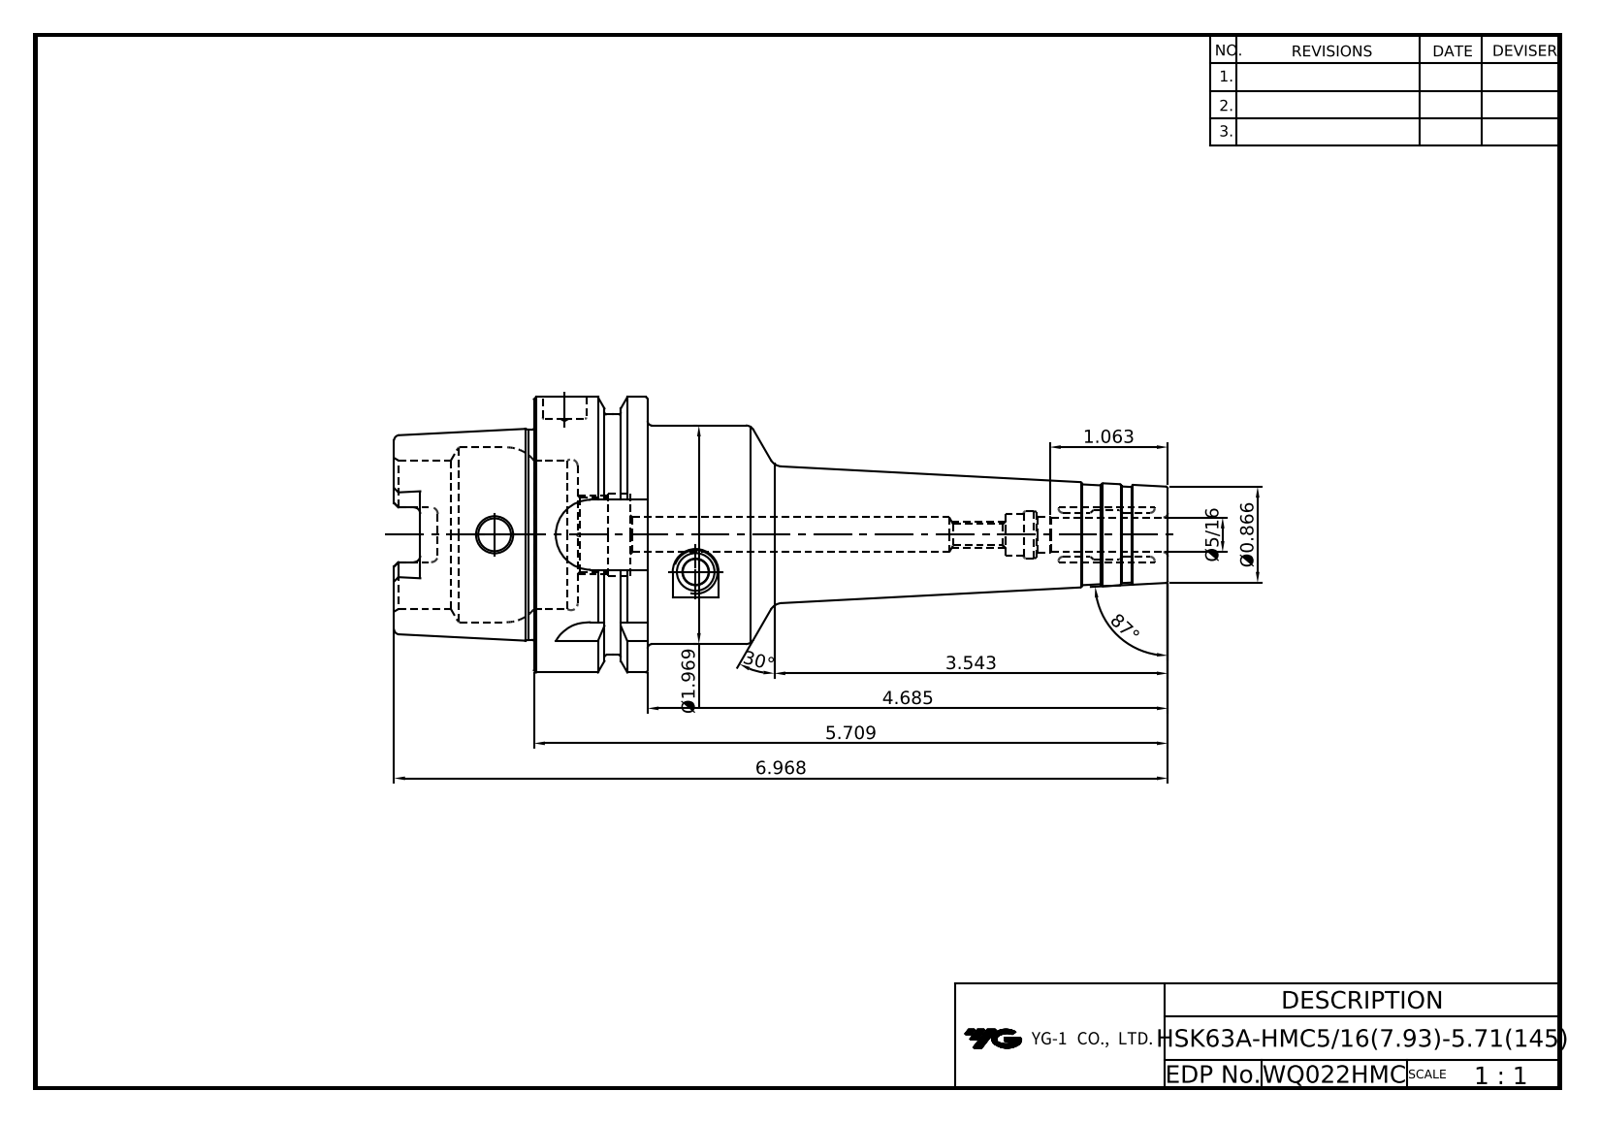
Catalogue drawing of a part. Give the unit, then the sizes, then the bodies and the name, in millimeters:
Units: millimetres
Overall size (bounding box): 177 × 63 × 63
Round holes (diameter × count): ⌀4.92 ×1, ⌀7.5 ×1, ⌀7.94 ×1, ⌀8 ×1, ⌀9.5 ×1, ⌀10 ×1, ⌀16.92 ×1, ⌀19 ×1, ⌀34 ×1, ⌀40 ×1
Round bosses / shafts (diameter × count): ⌀63 ×1, ⌀55 ×1, ⌀50 ×1, ⌀48.04 ×1
Partial cylindrical surfaces — rounded edges, fillets, slot ends (radius × count): R1.5 ×6, R2.88 ×4, R8 ×4
Main face-to-face distances: 26, 10, 16, 32, 42, 58, 4, 53, 22, 177
Volume: 180 091 mm³ · Surface area: 36 267 mm²
Bodies: 1 solid, 135 faces (42 planar, 34 cylindrical, 59 other)
Part name (STEP PRODUCT): LO-HSK63A-HMC7.9375-145
STEP written by: Autodesk Inventor 2020 (AUTOMOTIVE_DESIGN)
